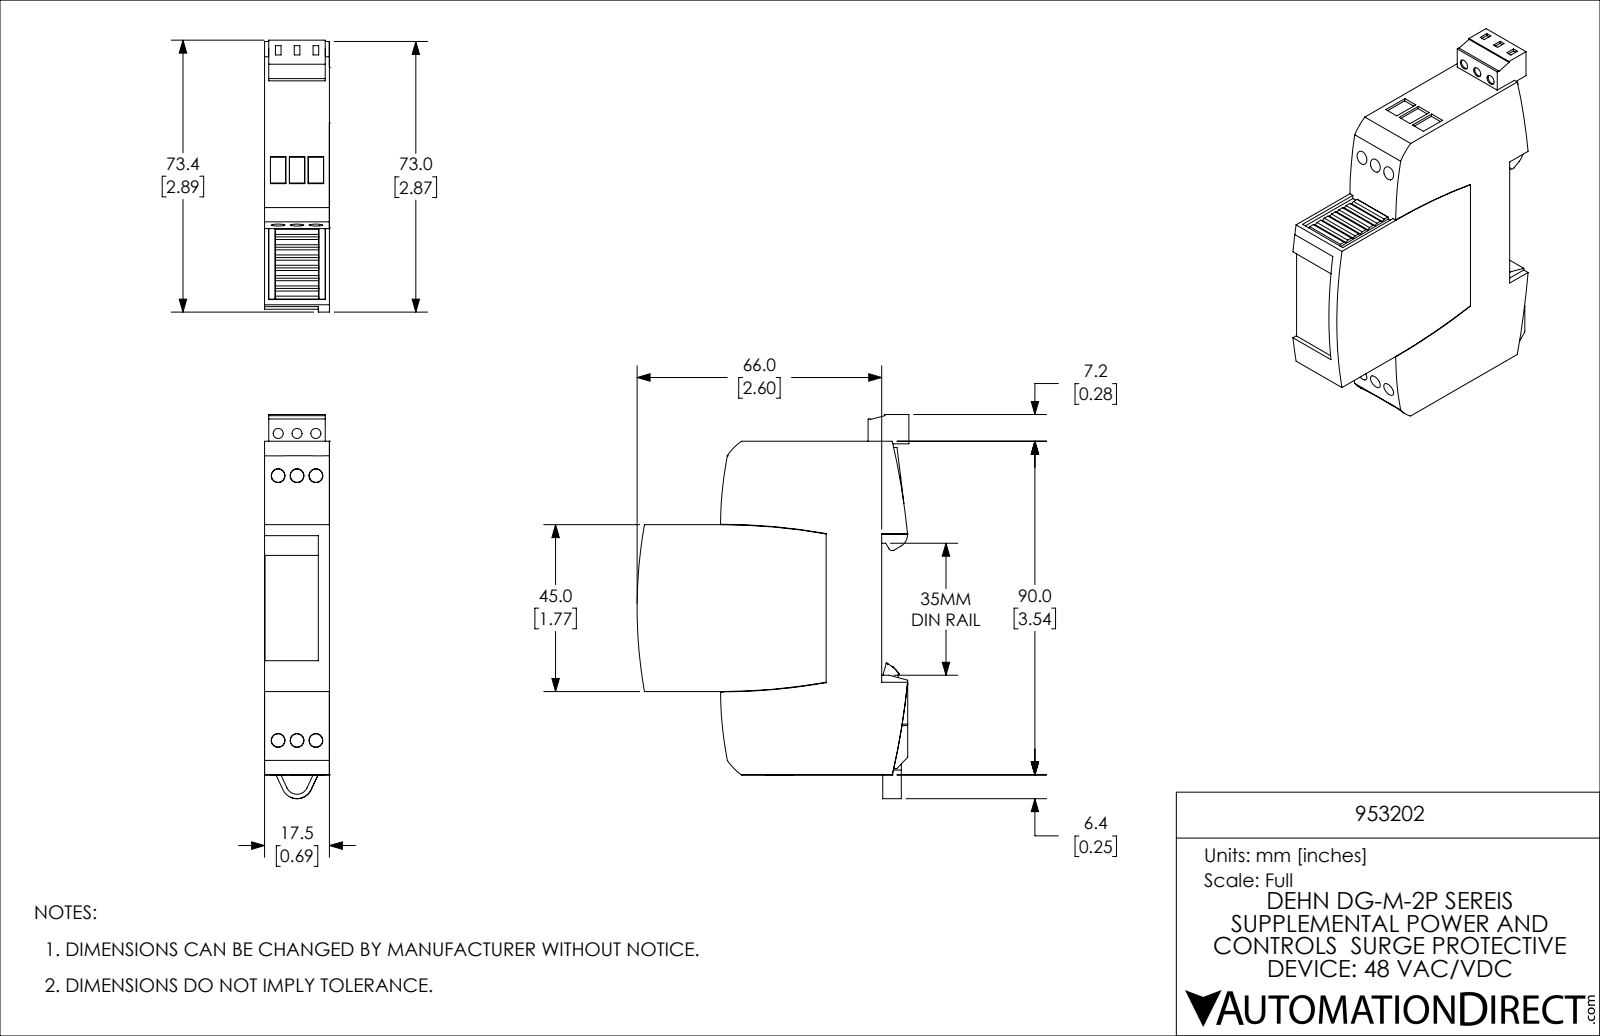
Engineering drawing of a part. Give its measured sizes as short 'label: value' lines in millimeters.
name: 953202
written by: SolidWorks 2019 (CONFIG_CONTROL_DESIGN)
unit: mm
bodies: 1 solid, 255 faces (198 planar, 38 cylindrical, 19 other)
size: 103.6 × 73.4 × 17.5
volume: 89 060 mm³; area: 17 550 mm²
holes: 3× ⌀2.7
rounds: 2× R163.8, 2× R163.8, 1× R1, 1× R2.5, 1× R3, 1× R3.5, 1× R100, 1× R100.1
face distances: 17.5, 17.4, 90, 0.4, 17.1, 64, 7, 71, 22.8, 67.2
hole spacings: 5.1, 10.2
